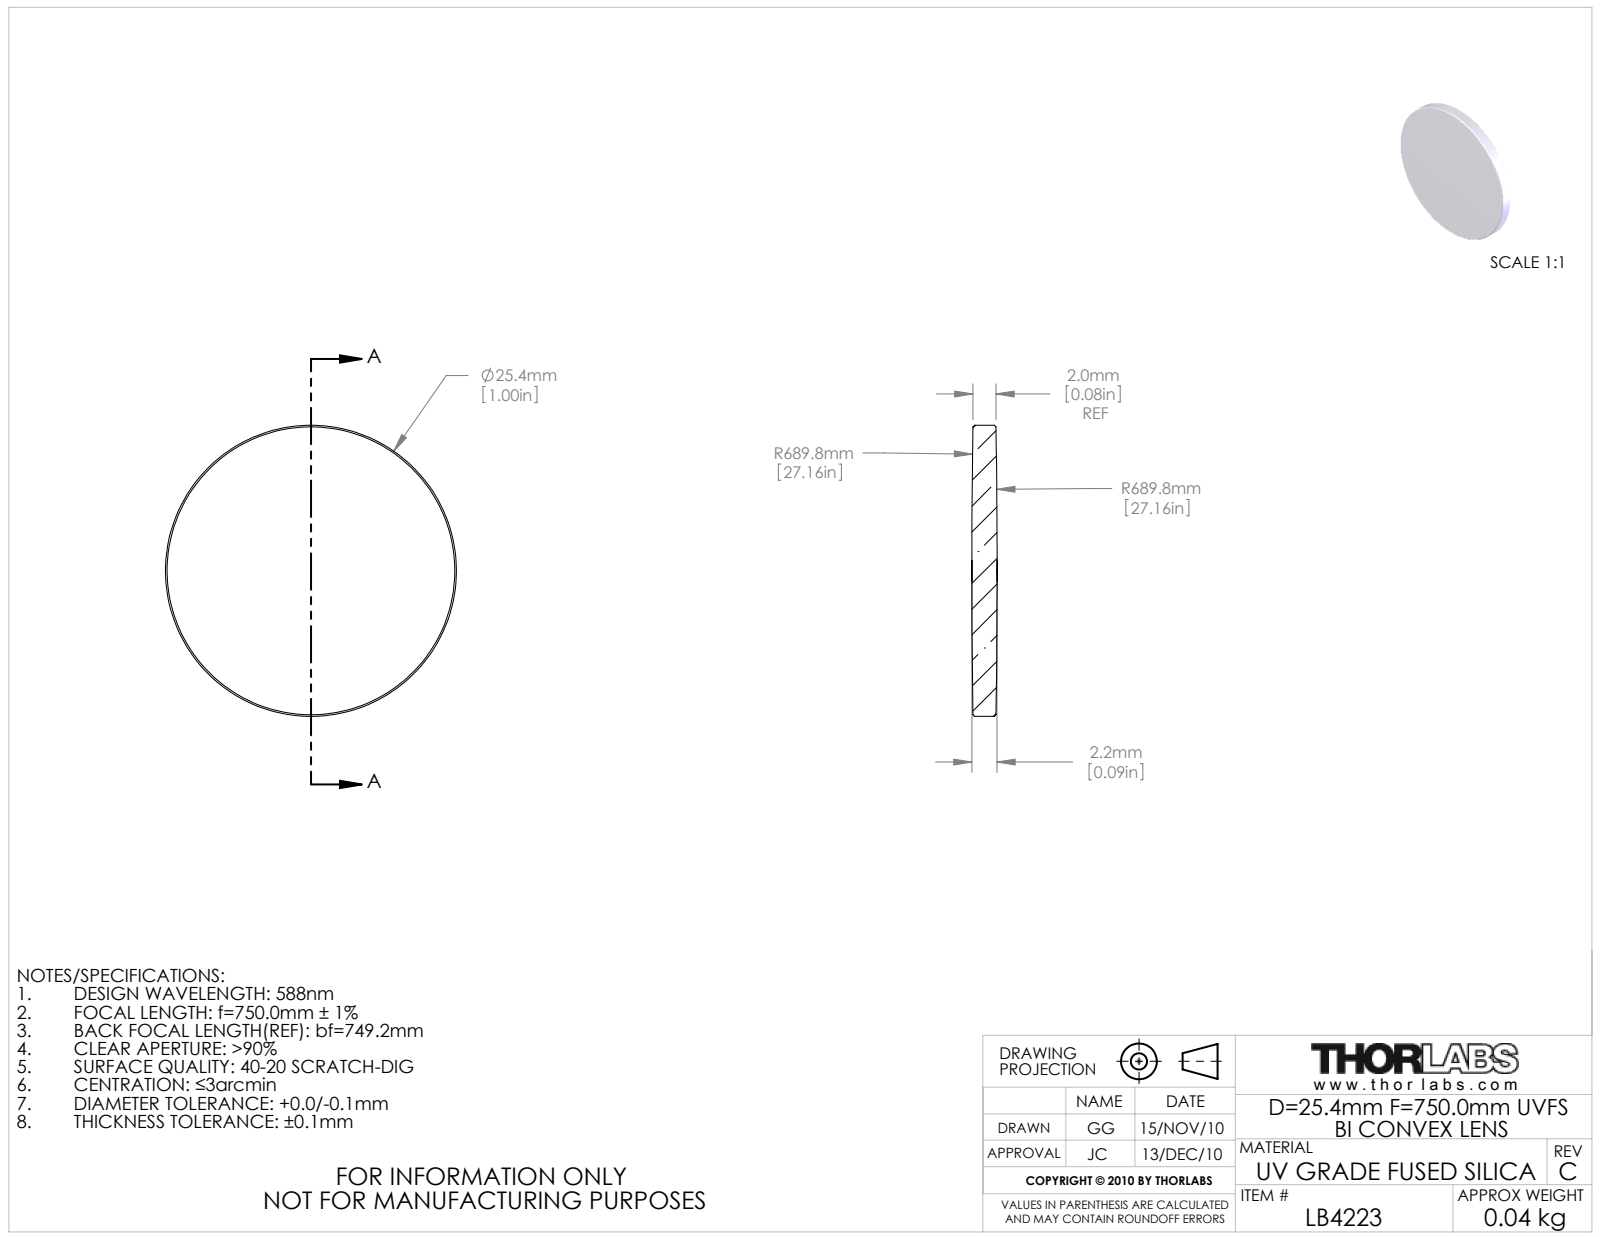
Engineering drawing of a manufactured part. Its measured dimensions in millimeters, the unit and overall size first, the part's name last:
Units: millimetres
Overall size (bounding box): 25.4 × 25.4 × 2.2
Round bosses / shafts (diameter × count): ⌀25.4 ×1
Volume: 1 065 mm³ · Surface area: 1 160 mm²
Bodies: 1 solid, 10 faces (0 planar, 2 cylindrical, 8 other)
Part name (STEP PRODUCT): 3411-E0W
STEP written by: SolidWorks 2009 (AUTOMOTIVE_DESIGN)
